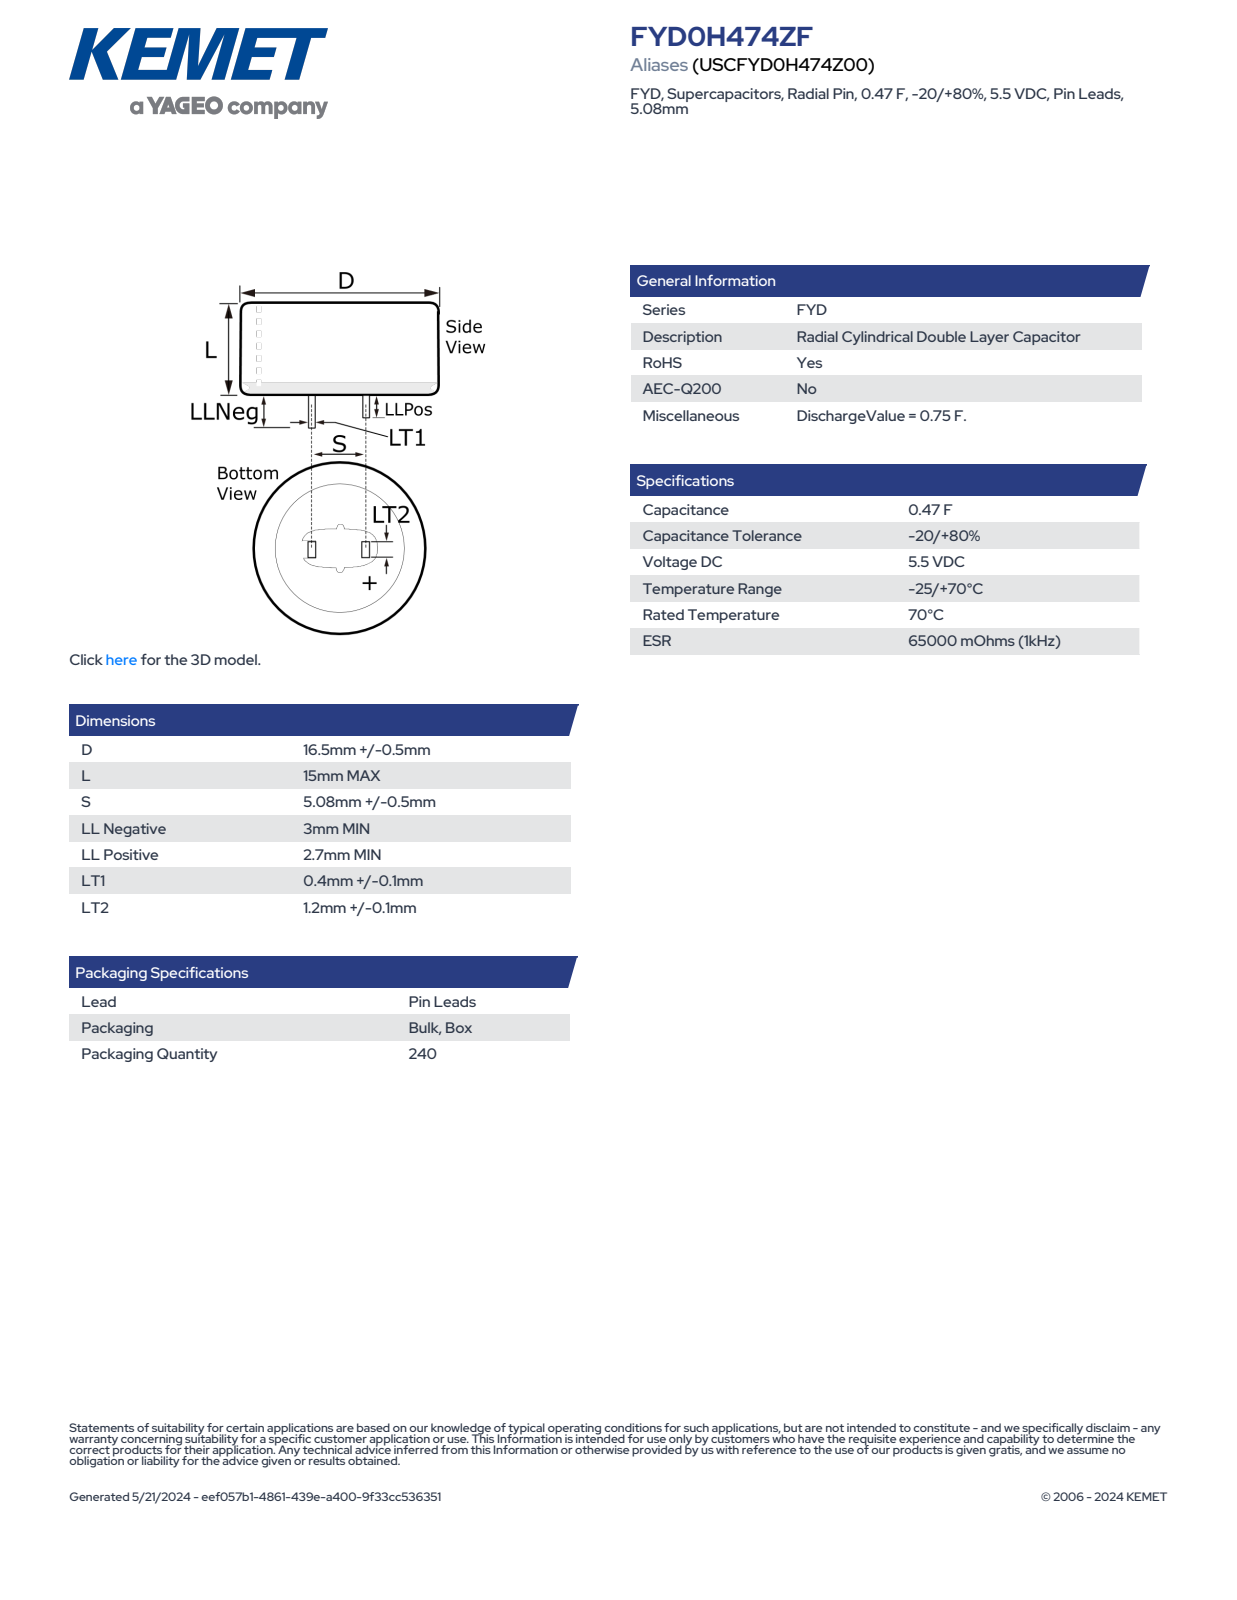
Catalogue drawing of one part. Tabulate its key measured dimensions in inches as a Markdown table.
| quantity | value |
| --- | --- |
| part name | CDR_LPLLN_D17L15S5.08LLNEG3LLPOS2.7LT10.5LT21.3 |
| STEP written by | SolidWorks 2014 (AUTOMOTIVE_DESIGN) |
| units | inches |
| bodies | 1 solid, 78 faces (70 planar, 4 cylindrical, 4 other) |
| overall size | 0.709 × 0.669 × 0.669 |
| volume | 0.207 in³ |
| surface area | 1.908 in² |
| round bosses / shafts (diameter × count) | 0.669 × 1 |
| partial cylindrical surfaces (radius × count) | 0.335 × 1 |
| main face-to-face distances | 0.591, 0.59, 0.02, 0.2, 0.22, 0.18, 0.051, 0.118, 0.708, 0.709 |
